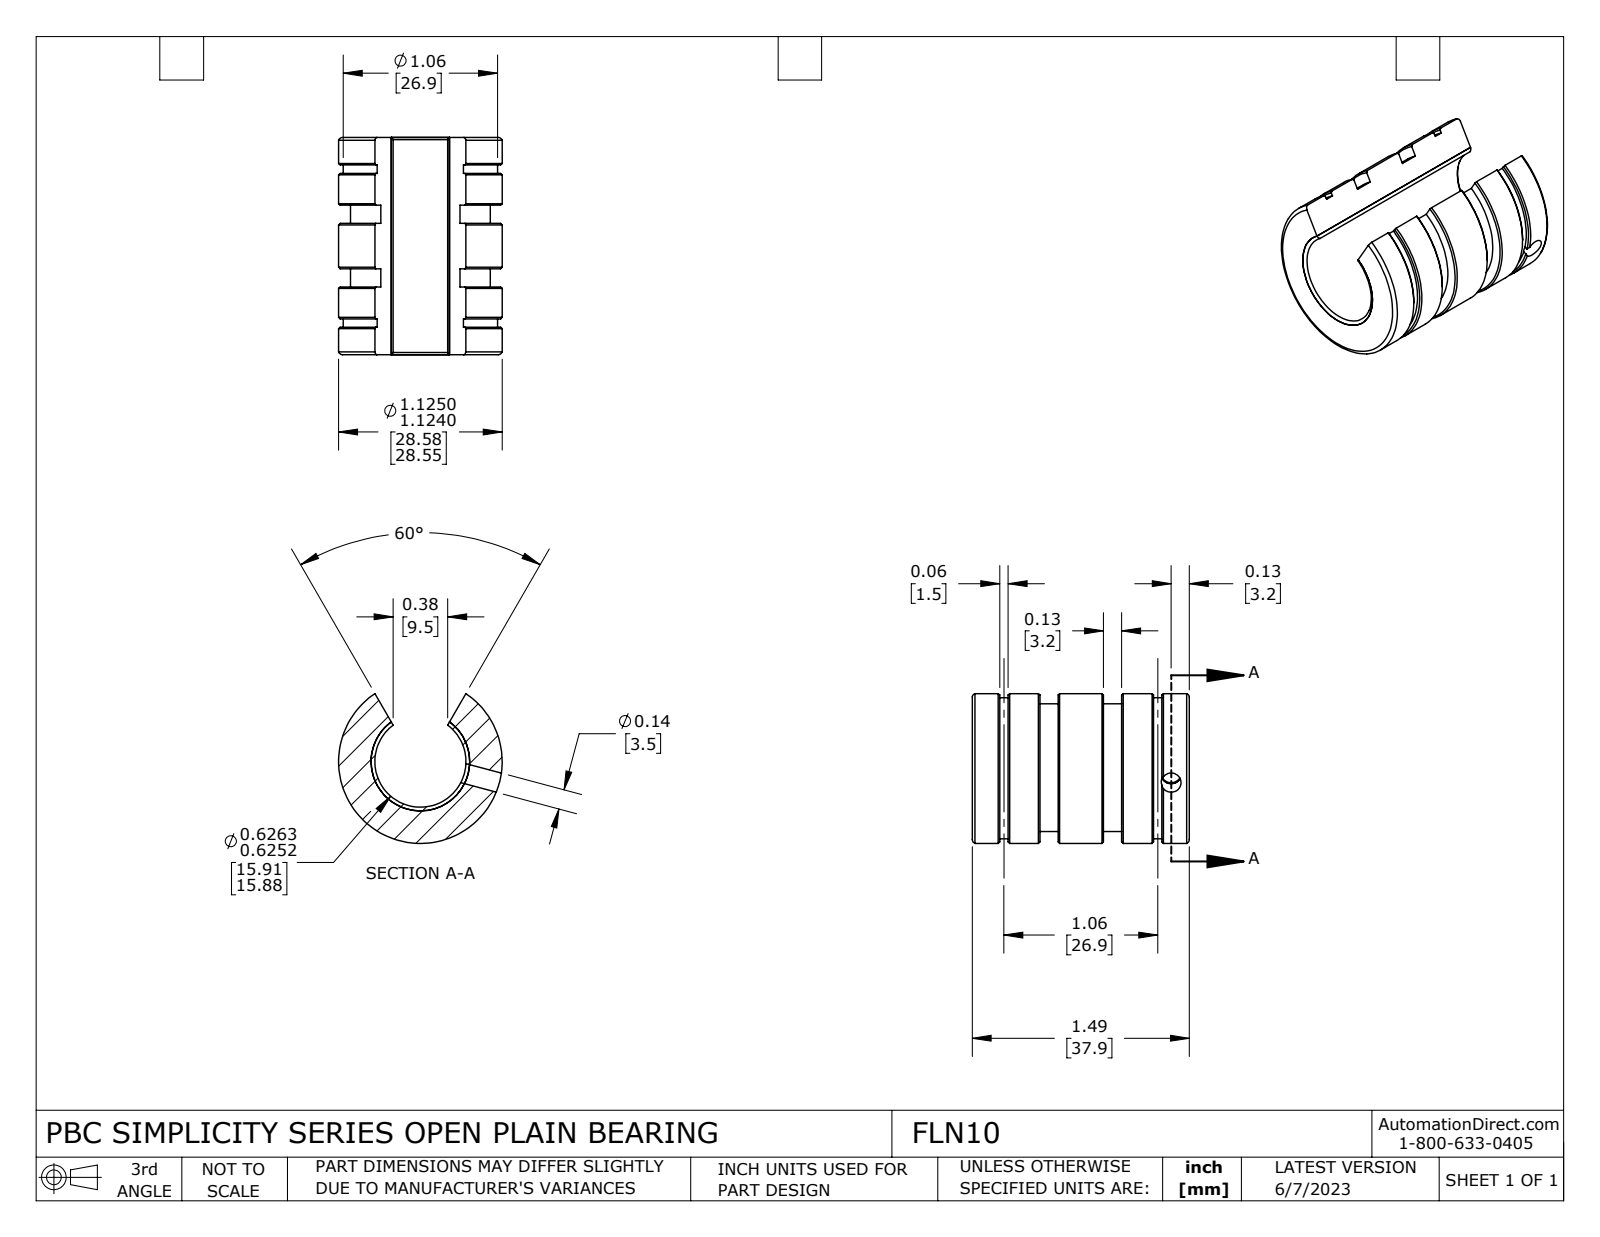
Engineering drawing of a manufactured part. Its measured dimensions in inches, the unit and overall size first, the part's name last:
Units: inches
Overall size (bounding box): 1.493 × 1.124 × 1.029
Round holes (diameter × count): ⌀0.136 ×1, ⌀0.626 ×1, ⌀0.677 ×1
Round bosses / shafts (diameter × count): ⌀1.124 ×1, ⌀1.06 ×1, ⌀0.962 ×1
Main face-to-face distances: 1.492, 0.59, 0.902, 0.465, 1.027, 0.125, 0.437, 0.312, 0.562, 0.246
Volume: 0.754 in³ · Surface area: 14.39 in²
Bodies: 2 solids, 83 faces (15 planar, 40 cylindrical, 28 other)
Part name (STEP PRODUCT): FLN10
STEP written by: SolidWorks 2021 (CONFIG_CONTROL_DESIGN)
